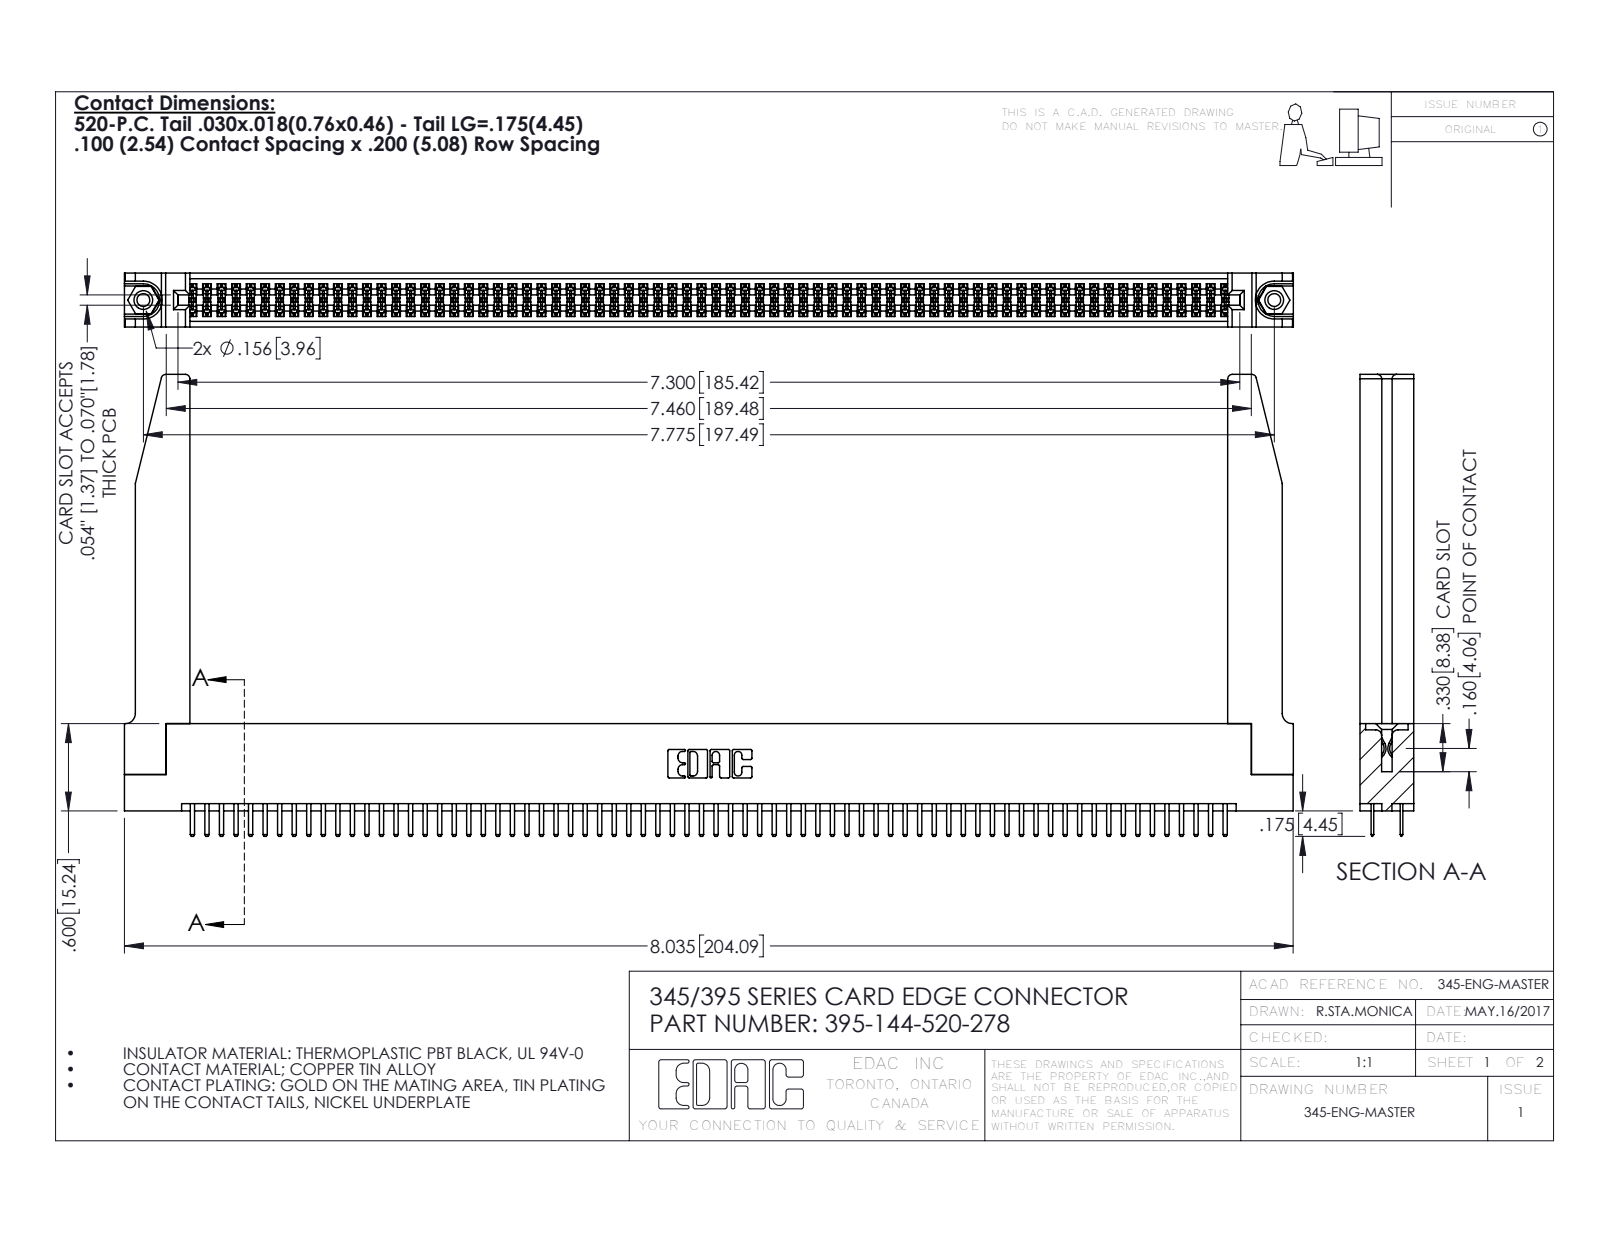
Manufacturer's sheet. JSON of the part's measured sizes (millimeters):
{"part_name": "345-292-001_345-293-120; 345-250-001_345-250-001-102; 395-144-520-278; 345 Part_Flush Mounting Lugs - 0.156 Dia-TH (+1 more)", "step_written_by": "SolidWorks 2016 (CONFIG_CONTROL_DESIGN)", "units": "millimeters", "bodies": {"solids": 149, "faces": 8136, "planar": 5262, "cylindrical": 2822, "other": 52}, "overall_size": [204.1, 80.6, 9.4], "volume_mm3": 27810, "surface_area_mm2": 36910, "round_holes": [[2.3, 2], [3.2, 2], [4, 2], [1.6, 1]], "round_bosses_or_shafts": [[3.9, 2]], "partial_cylinders_radius": [[0.2, 216], [0.3, 148], [0.3, 22], [0.8, 8], [0.2, 6], [0.8, 6], [0.7, 3], [0.4, 2]], "face_to_face_distances": [1.8, 7.6, 9.4, 5.1, 2.5, 6.9, 0.6, 5.7, 0.6, 1.8], "hole_center_spacings": [6.9, 191.5, 197.5]}
